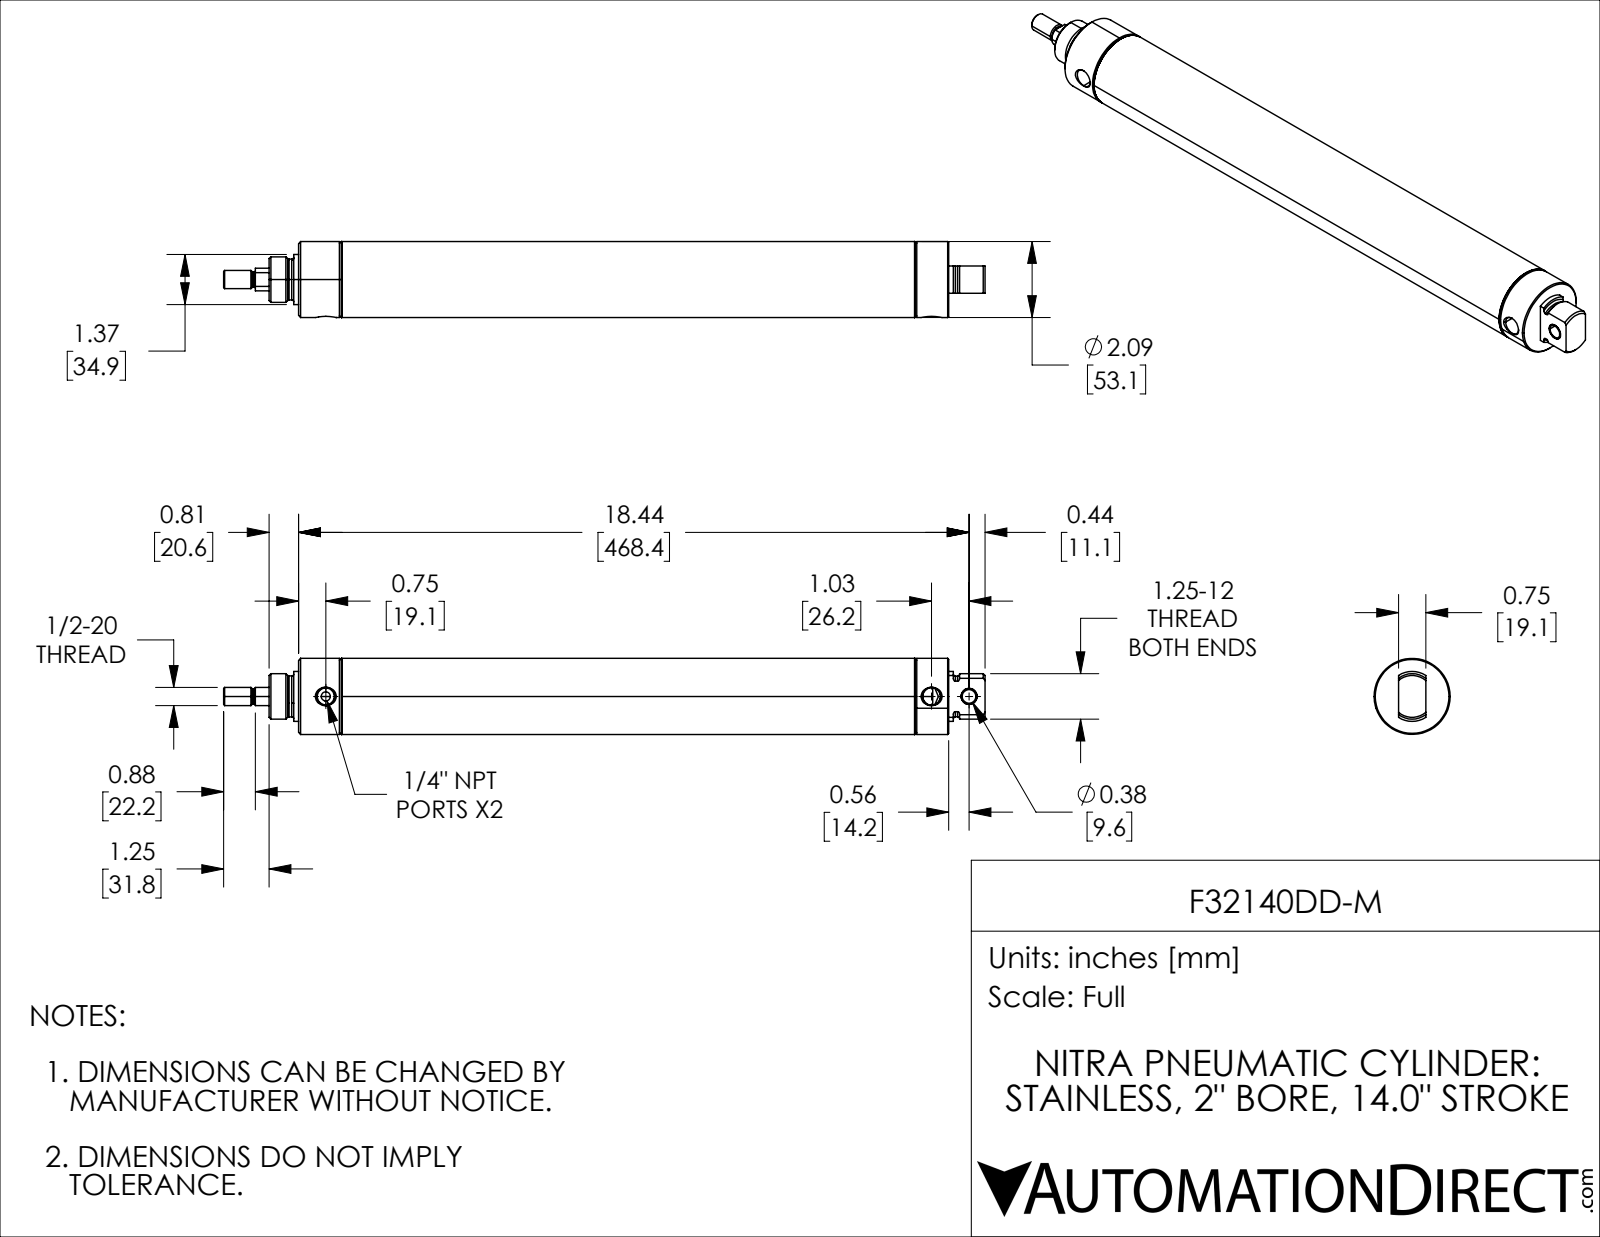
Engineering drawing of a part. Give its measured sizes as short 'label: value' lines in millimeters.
name: F32140DD-M_5; F32140DD-M_11; F32140DD-M_7; F32140DD-M_3 (+2 more)
written by: SolidWorks 2021 (CONFIG_CONTROL_DESIGN)
unit: mm
bodies: 5 solids, 160 faces (31 planar, 60 cylindrical, 69 other)
size: 531.83 × 53.09 × 53.09
volume: 362 347 mm³; area: 196 240 mm²
holes: 1× ⌀6.35, 1× ⌀9.55, 1× ⌀11.15, 1× ⌀12.18, 1× ⌀16.52, 1× ⌀19.05, 1× ⌀49.05
bosses: 1× ⌀53.09, 1× ⌀51.16, 1× ⌀34.87, 1× ⌀31.75, 1× ⌀28.51, 1× ⌀15.88, 1× ⌀12.7, 1× ⌀10.46
rounds: 1× R14.25
face distances: 30.17, 355.6, 385.77, 416, 60.4, 30.23, 385.78, 30.18, 30.22, 38.15
hole spacings: 26.16, 423.16, 449.32
